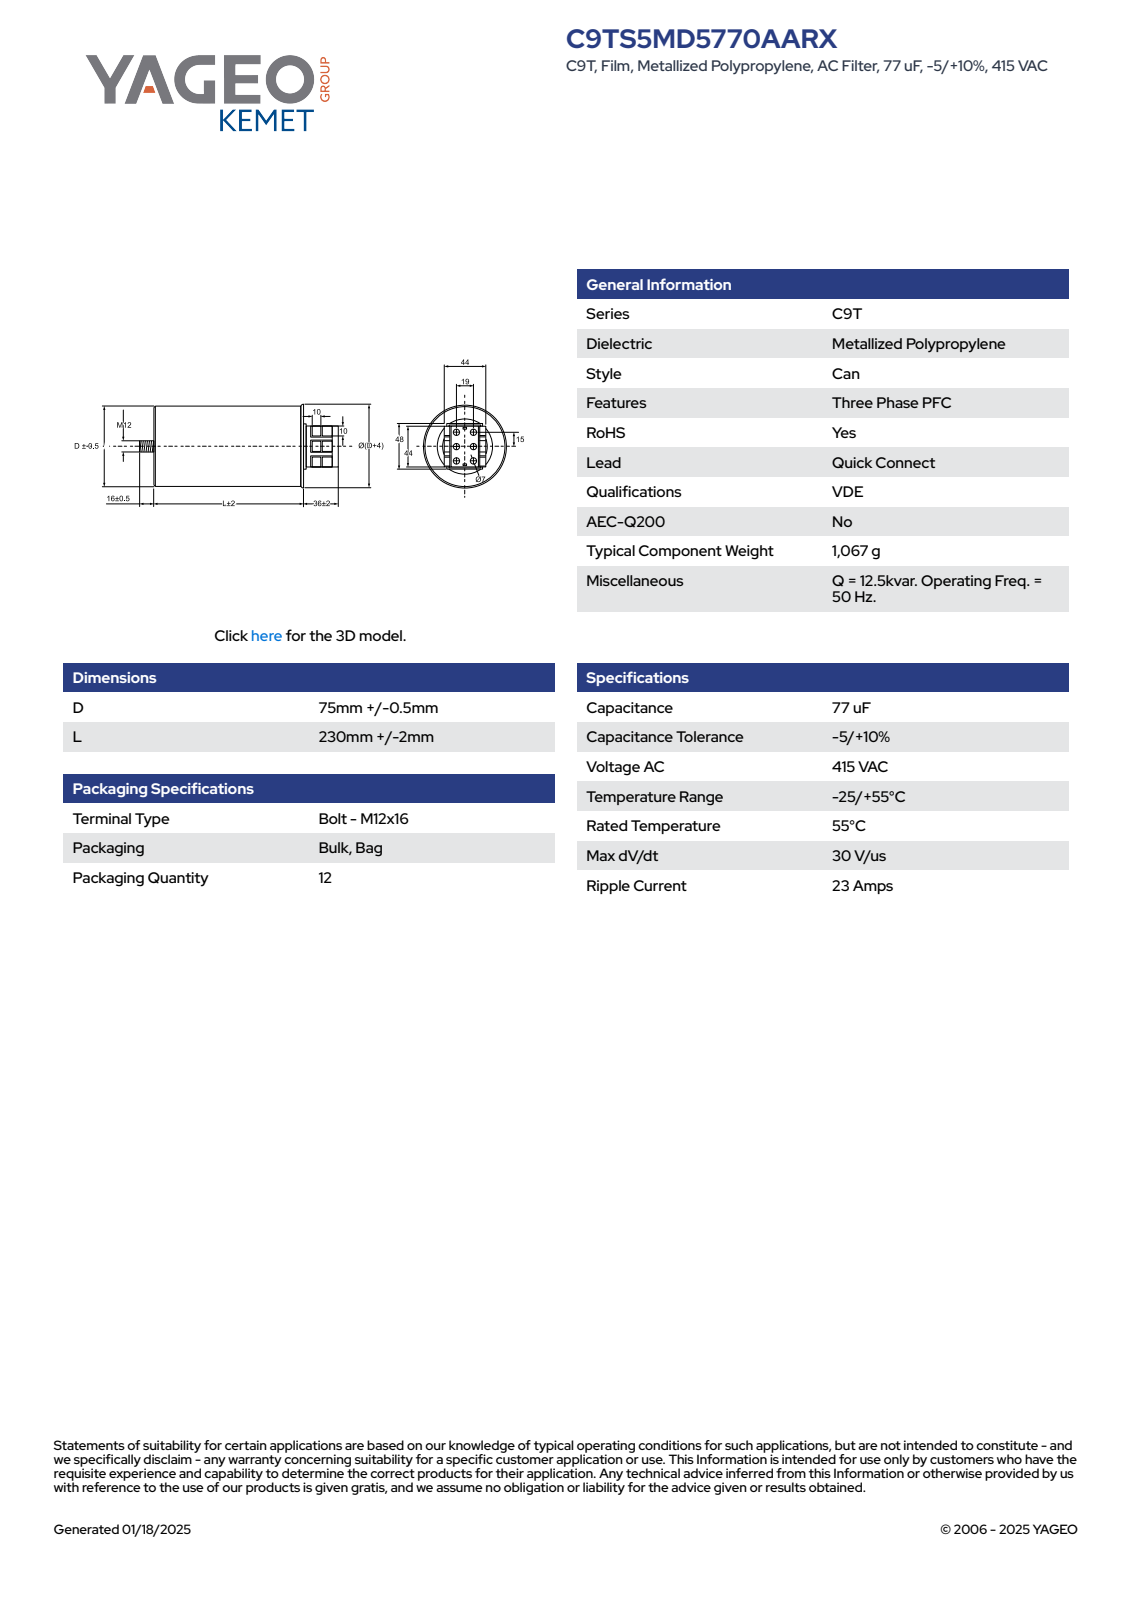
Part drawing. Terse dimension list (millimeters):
name: CFP_C9T_75X230_D75.5L232
written by: SolidWorks 2014 (AUTOMOTIVE_DESIGN)
unit: mm
bodies: 1 solid, 138 faces (78 planar, 25 cylindrical, 35 other)
size: 286.5 × 79.5 × 79.5
volume: 1 076 000 mm³; area: 86 233 mm²
holes: 6× ⌀7
bosses: 1× ⌀75.5, 1× ⌀12
rounds: 1× R37.76
face distances: 10, 11.15, 232, 15.85, 1.15, 4, 44, 236, 38, 17
hole spacings: 15, 24.21, 19, 30, 35.51
